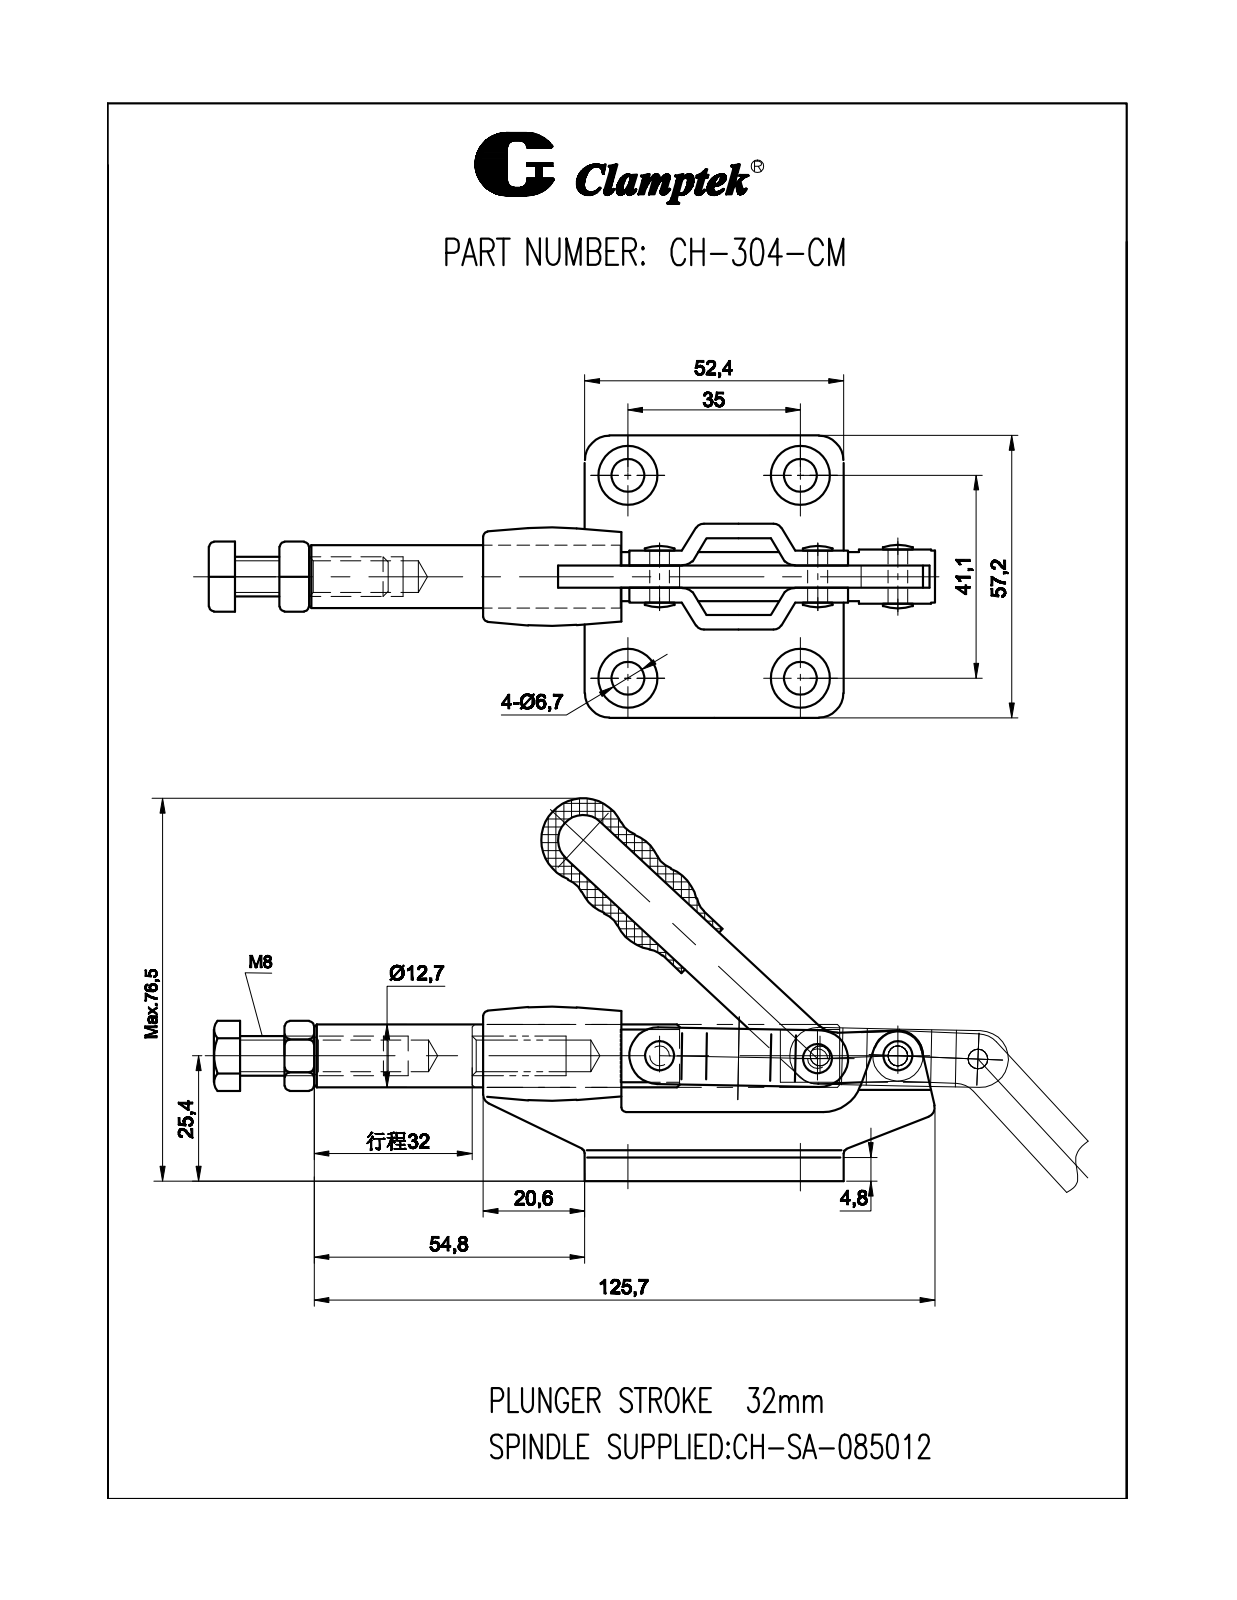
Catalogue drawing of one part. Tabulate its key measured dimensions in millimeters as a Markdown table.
| quantity | value |
| --- | --- |
| part name | CH-304-CM |
| STEP written by | SolidWorks 2008 (CONFIG_CONTROL_DESIGN) |
| units | millimeters |
| bodies | 11 solids, 795 faces (247 planar, 266 cylindrical, 282 other) |
| overall size | 153.75 × 79.3 × 57.2 |
| volume | 52 750 mm³ |
| surface area | 30 251 mm² |
| round holes (diameter × count) | 6.8 × 5, 12 × 4, 3.02 × 3, 4 × 3, 0.76 × 1, 6.5 × 1, 12.7 × 1 |
| round bosses / shafts (diameter × count) | 8 × 1, 0.67 × 1 |
| partial cylindrical surfaces (radius × count) | 0.5 × 12, 3 × 8, 0.2 × 6, 1 × 6, 5 × 6, 5.1 × 2, 5.75 × 2, 1.5 × 1 |
| main face-to-face distances | 4.5, 2.75, 7.25, 10, 3, 13, 5.5, 10.2, 7.5, 10.25 |
| hole center spacings | 35, 41.1, 53.98, 14.06, 16.25, 22.26, 28.56, 32 |
